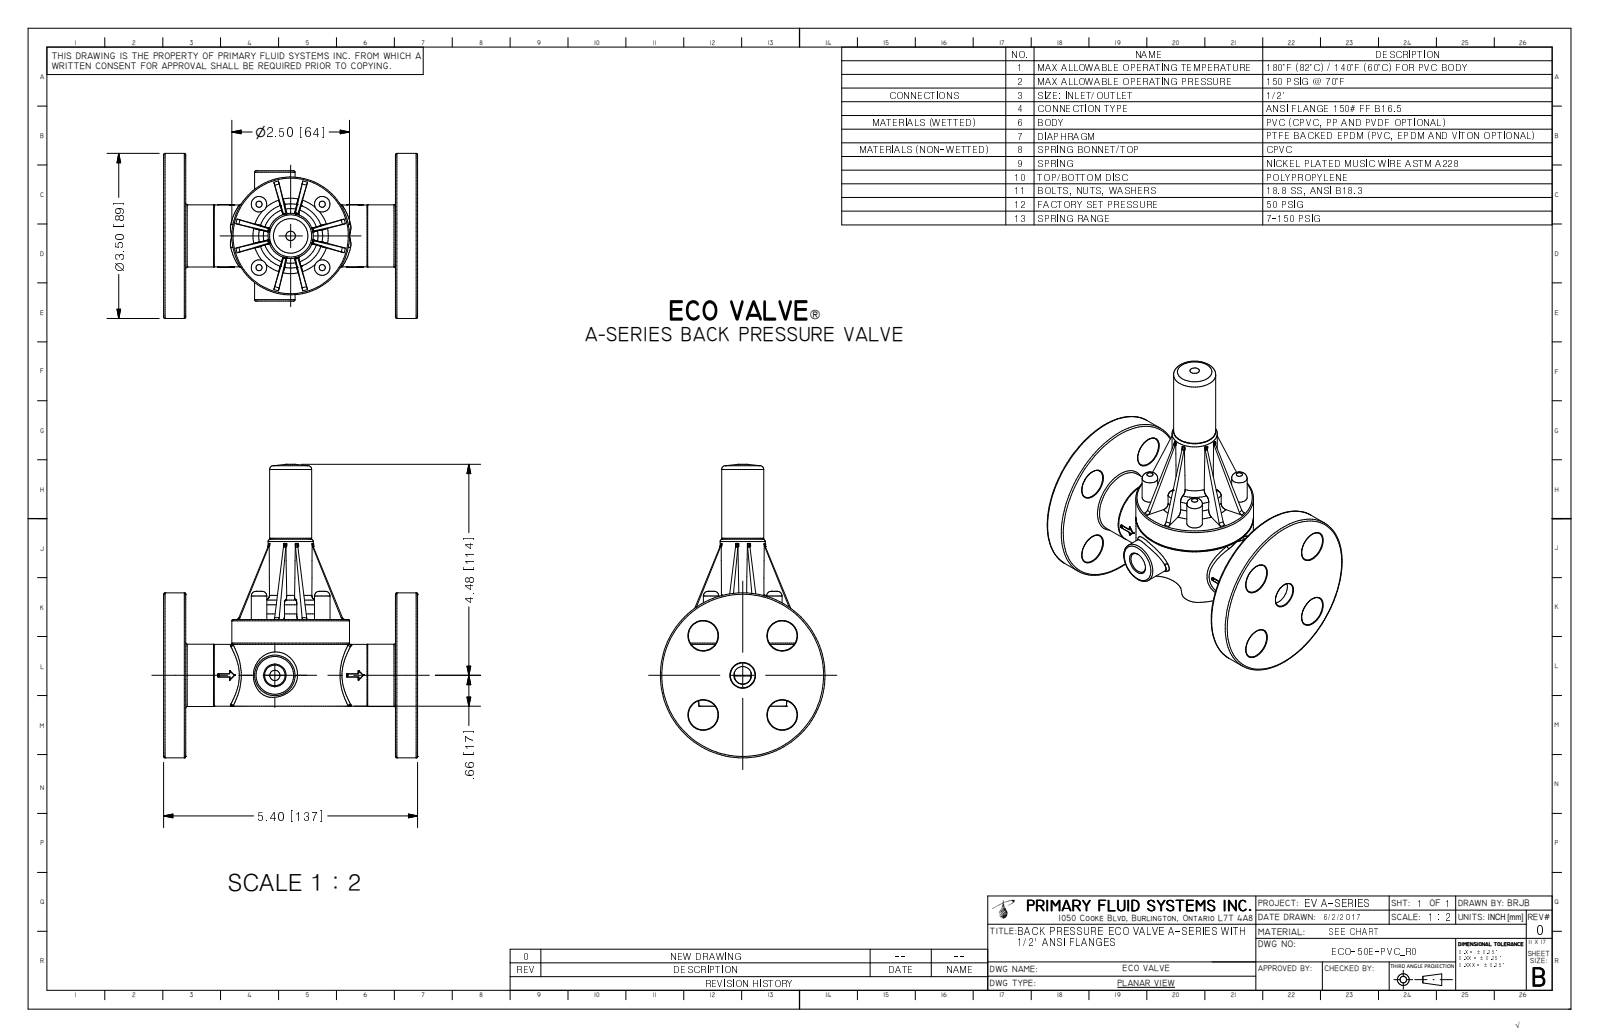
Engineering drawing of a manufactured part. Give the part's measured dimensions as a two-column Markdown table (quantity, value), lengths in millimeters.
| quantity | value |
| --- | --- |
| part name | ECO-50E-PVC_R0 |
| STEP written by | Autodesk Inventor 2009 (AUTOMOTIVE_DESIGN) |
| units | millimeters |
| bodies | 1 solid, 365 faces (128 planar, 85 cylindrical, 152 other) |
| overall size | 158.1 × 137.2 × 88.9 |
| volume | 344 900 mm³ |
| surface area | 83 740 mm² |
| round holes (diameter × count) | 5.8 × 4, 6.5 × 4, 10.2 × 4, 16 × 4, 11.1 × 1, 13.4 × 1 |
| round bosses / shafts (diameter × count) | 8.4 × 4, 6.5 × 4, 88.9 × 1, 63.5 × 1, 34.5 × 1, 33.5 × 1, 33.4 × 1, 24.4 × 1 |
| partial cylindrical surfaces (radius × count) | 1.8 × 8, 2.5 × 8, 3.3 × 4, 16.9 × 1, 23.3 × 1, 27.1 × 1 |
| main face-to-face distances | 11.9, 125.2, 137.2, 113.3, 46.7, 33.4, 13.3, 5.1, 28.3, 41.6 |
| hole center spacings | 34.1, 48.3, 34.1, 34.1, 30.1, 30.2, 42.6, 42.7 |
